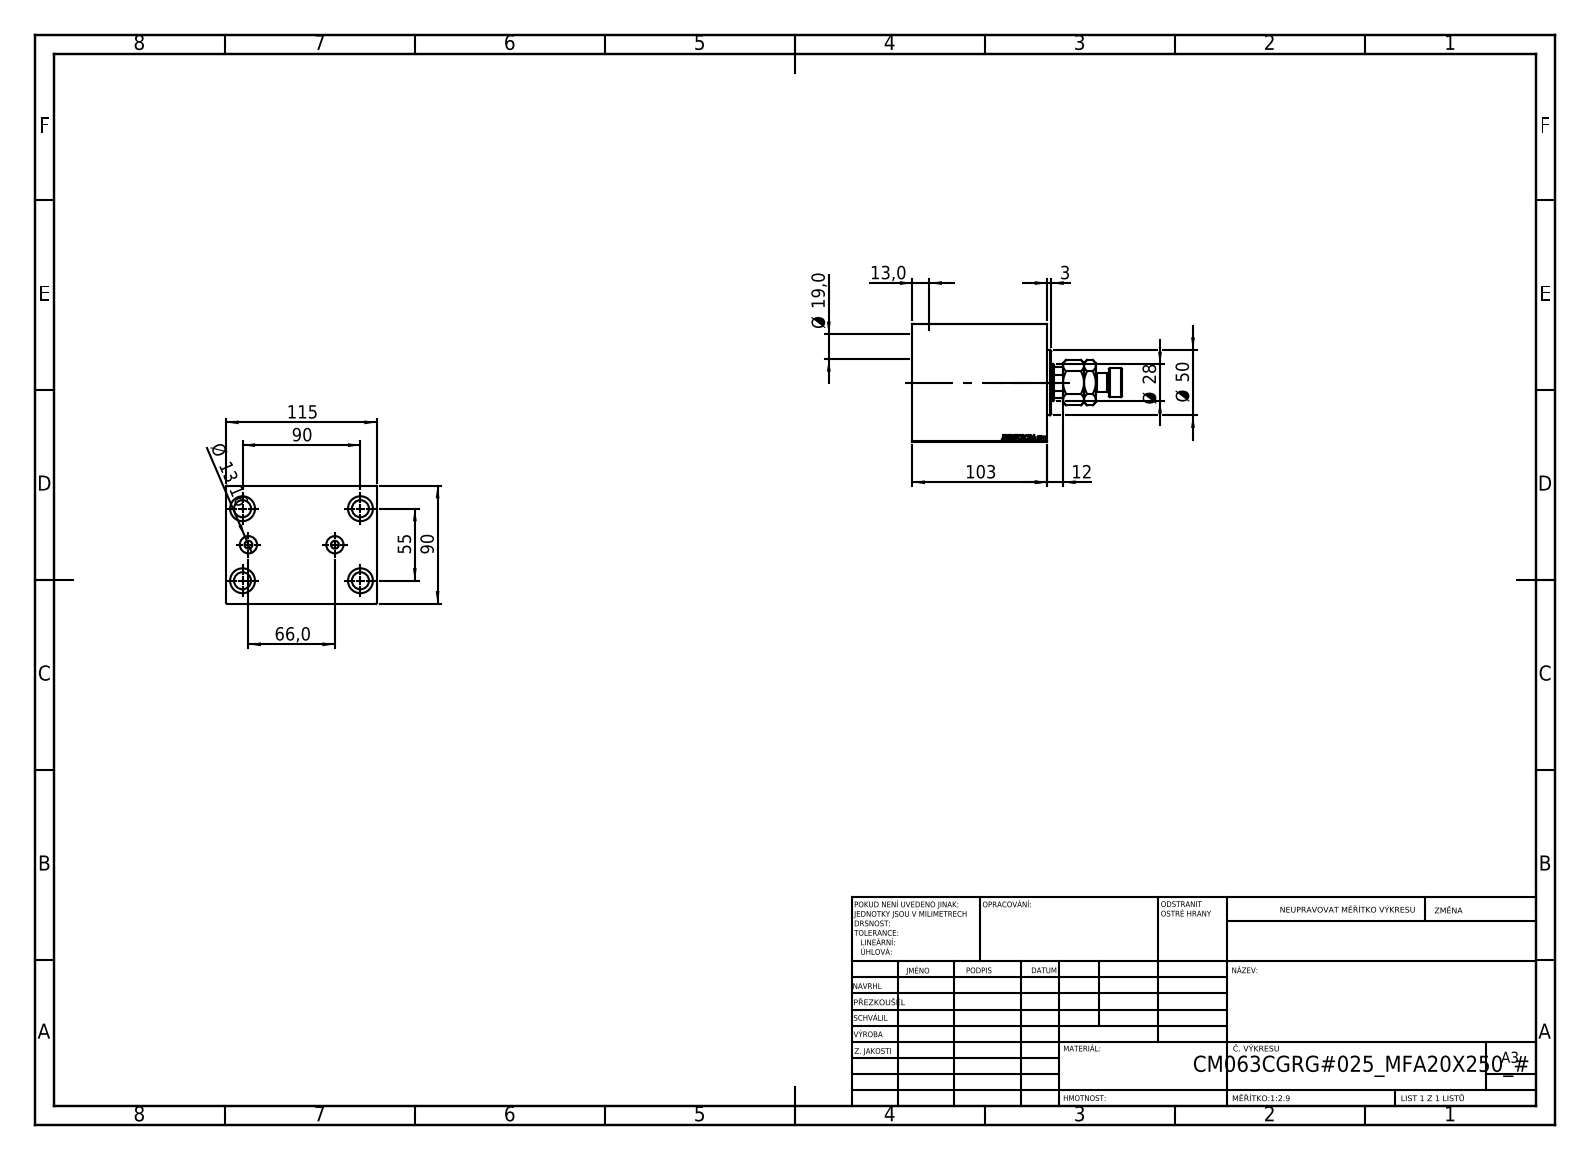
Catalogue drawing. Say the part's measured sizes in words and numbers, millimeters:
The part is named "V450CM_VC_B; V450CM_C_VCP; MFA; V450CM_C_Body". Its 3-D file was written by "SolidWorks 2019 (CONFIG_CONTROL_DESIGN)". It is 4 solids with 912 faces: 424 planar, 62 cylindrical and 426 other. Overall it measures 160 by 115 by 90 millimeters. Its volume is 991 940 cubic millimeters and its surface area 129 023 square millimeters. Round holes: 4 of diameter 13, 4 of diameter 19, 2 of diameter 6, 2 of diameter 13.16, 1 of diameter 18.5, 1 of diameter 28, 1 of diameter 31.5, 1 of diameter 63, 1 of diameter 65, 1 of diameter 72. Round bosses or shafts: 1 of diameter 50, 1 of diameter 22, 1 of diameter 14. Partial cylindrical surfaces (rounded edges, fillets, slot ends): 1 of radius 13.5. The main face-to-face distances are 90, 115, 103, 52, 51, 10, 21.6, 29.4, 81.4, 71.4. The hole center spacings are 52.74, 27.87, 33.71, 55, 75.67, 89.81, 90, 105.48.
